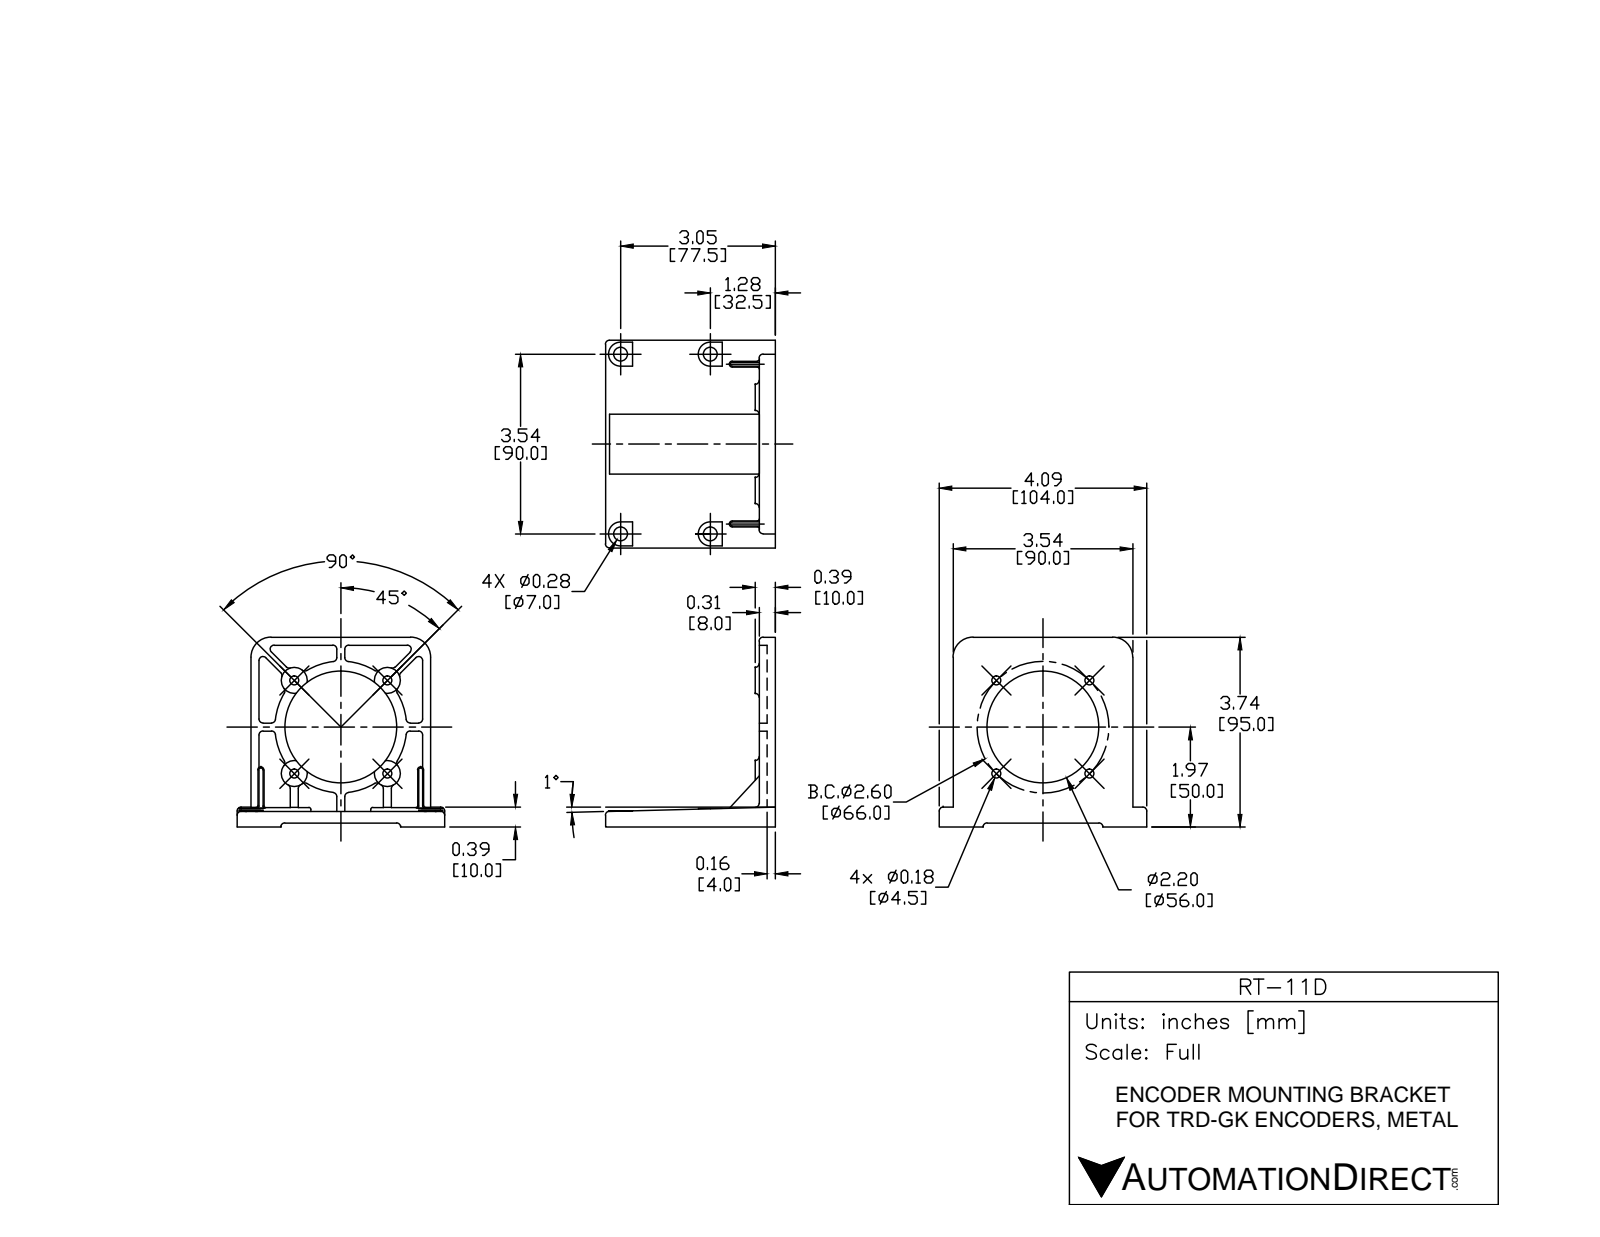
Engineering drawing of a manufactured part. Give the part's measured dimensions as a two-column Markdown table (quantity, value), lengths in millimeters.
| quantity | value |
| --- | --- |
| part name | RT-11D |
| STEP written by | SolidWorks 2016 (AUTOMOTIVE_DESIGN) |
| units | millimeters |
| bodies | 1 solid, 597 faces (111 planar, 175 cylindrical, 311 other) |
| overall size | 105.04 × 95 × 85 |
| volume | 86 441 mm³ |
| surface area | 41 115 mm² |
| round holes (diameter × count) | 56 × 1 |
| partial cylindrical surfaces (radius × count) | 2 × 54, 1 × 30, 0.5 × 20, 1.5 × 15, 0.3 × 8, 1.95 × 6, 6 × 5, 10 × 2 |
| main face-to-face distances | 4, 2.7, 8, 77, 81, 85, 63.94, 75, 2, 6 |
